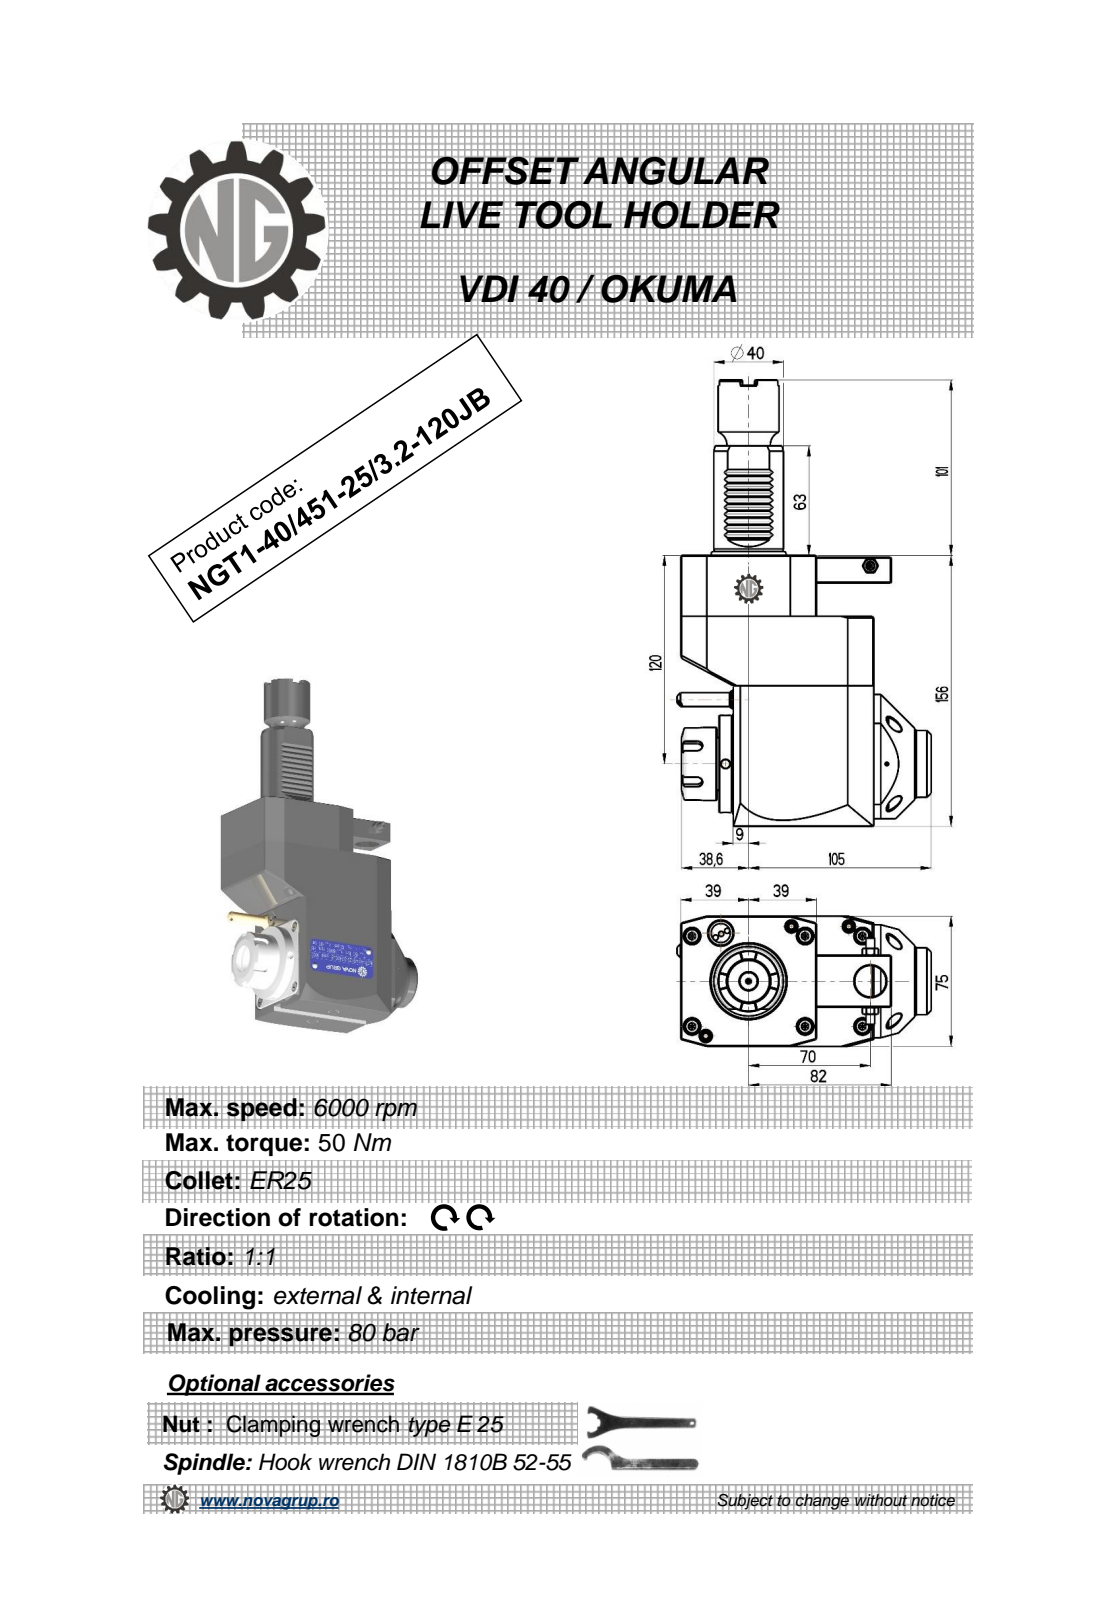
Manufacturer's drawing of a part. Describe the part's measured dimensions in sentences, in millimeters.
The part is named "NGT1_40_451_25_3_2_120JB". Its 3-D file was written by "PRO/ENGINEER BY PARAMETRIC TECHNOLOGY CORPORATION, 2010280 (CONFIG_CONTROL_DESIGN)". It is 1 solid with 492 faces: 217 planar, 89 cylindrical and 186 other. Overall it measures 257 by 146.14 by 75 millimeters. Its volume is 1 241 000 cubic millimeters and its surface area 95 440 square millimeters. Round holes: 3 of diameter 5, 1 of diameter 3, 1 of diameter 4.2, 1 of diameter 9.5, 1 of diameter 18, 1 of diameter 20.3, 1 of diameter 25. Round bosses or shafts: 1 of diameter 56, 1 of diameter 43, 1 of diameter 42, 1 of diameter 40, 1 of diameter 38.5, 1 of diameter 35, 1 of diameter 33, 1 of diameter 10. Partial cylindrical surfaces (rounded edges, fillets, slot ends): 12 of radius 0.26, 10 of radius 0.3, 6 of radius 0.2, 5 of radius 3, 1 of radius 0.5, 1 of radius 40. The main face-to-face distances are 75, 156, 111, 121, 33, 30, 35, 81, 93.43, 78. The hole center spacings are 13.25, 40.93, 70, 77.5, 83.25, 112.5, 141.16.
